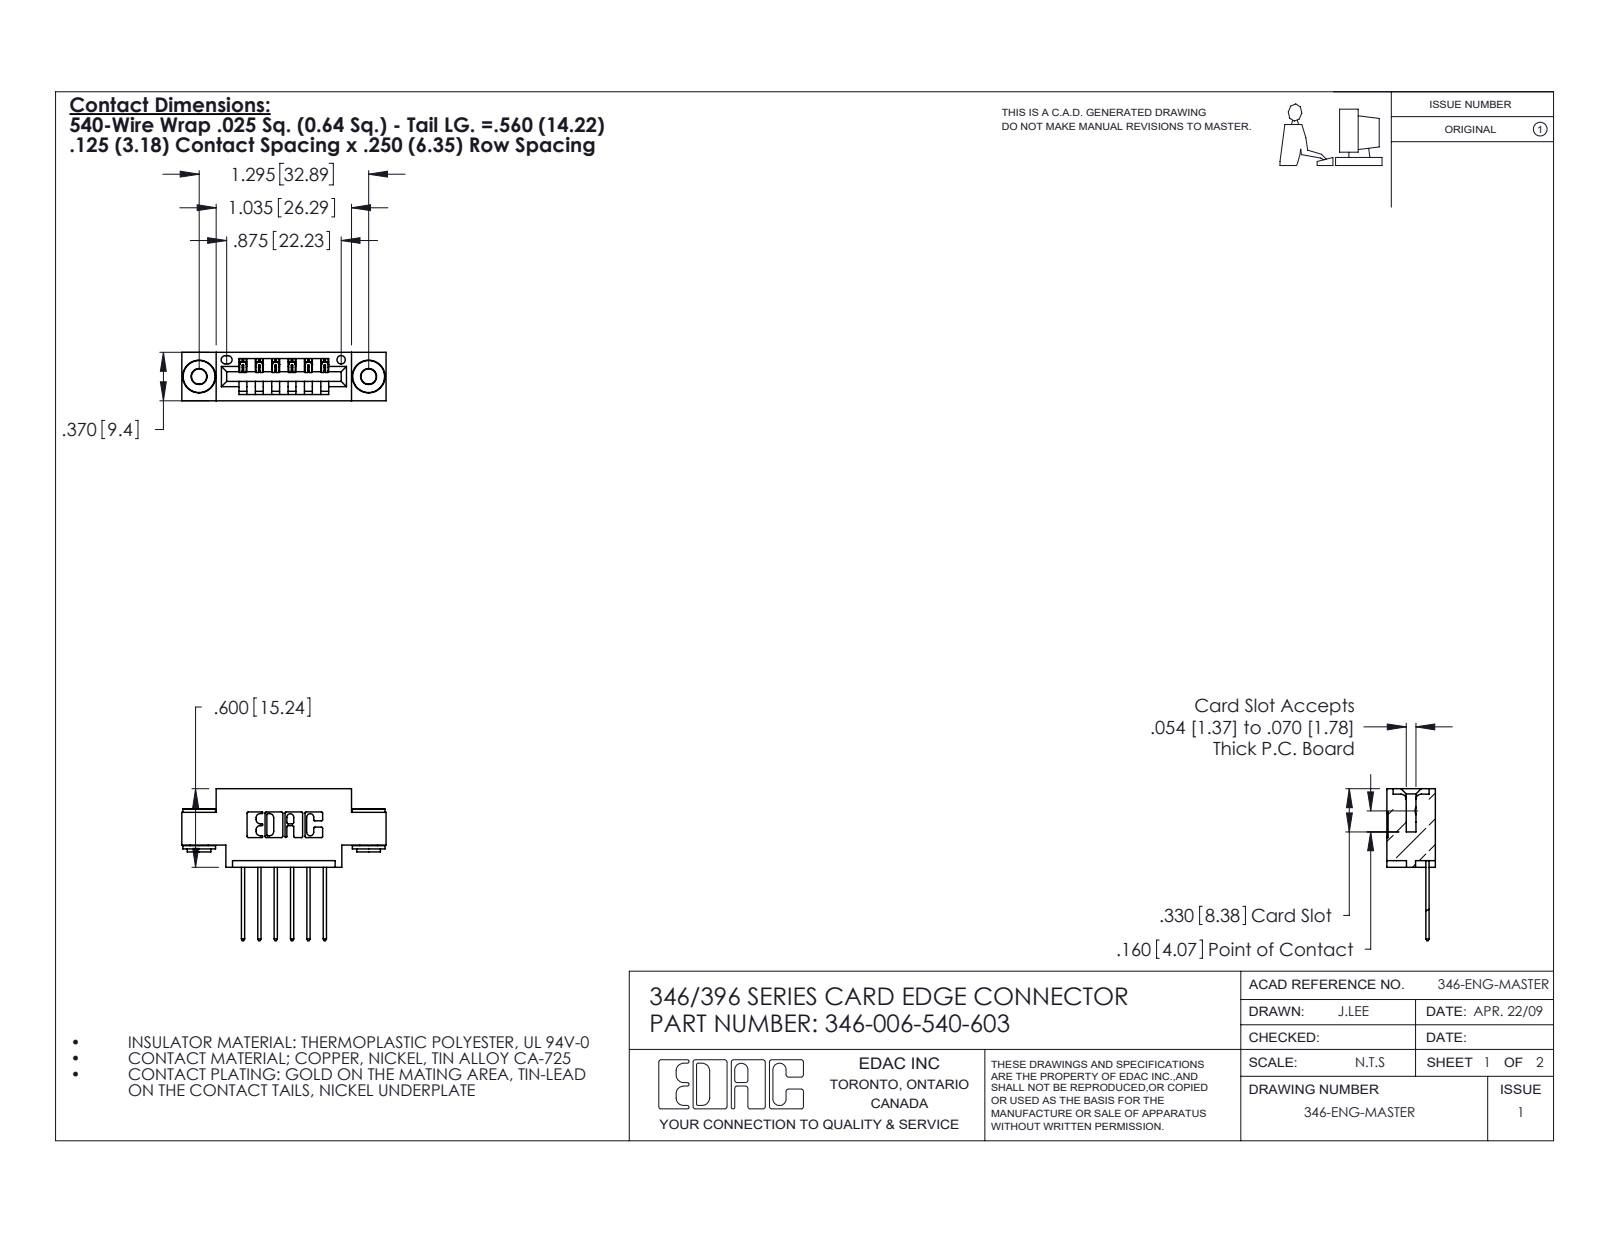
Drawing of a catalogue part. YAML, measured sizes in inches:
part_name: "345-292-001_345-293-140; 346 Part_0.170 Offset - 0.156 Dia-TH; 345-250-002_345-250-002-102; 346-006-540-603"
step_written_by: "SolidWorks 2020 (CONFIG_CONTROL_DESIGN)"
units: inches
bodies: {solids: 9, faces: 526, planar: 344, cylindrical: 174, other: 8}
overall_size: [1.56, 1.16, 0.37]
volume: 0.207
surface_area: 6.714
round_holes:
  - {diameter: 0.116, count: 2}
  - {diameter: 0.156, count: 2}
  - {diameter: 0.064, count: 1}
round_bosses_or_shafts:
  - {diameter: 0.25, count: 2}
  - {diameter: 0.18, count: 2}
  - {diameter: 0.136, count: 2}
partial_cylinders:
  - {radius: 0.01, count: 22}
  - {radius: 0.006, count: 12}
  - {radius: 0.01, count: 12}
  - {radius: 0.007, count: 6}
  - {radius: 0.031, count: 6}
  - {radius: 0.026, count: 3}
  - {radius: 0.031, count: 2}
  - {radius: 0.04, count: 2}
face_to_face_distances: [0.25, 0.37, 0.048, 0.322, 0.025, 0.222, 0.072, 0.298, 0.148, 0.1]
hole_center_spacings: [0.246, 1.092, 1.295]
